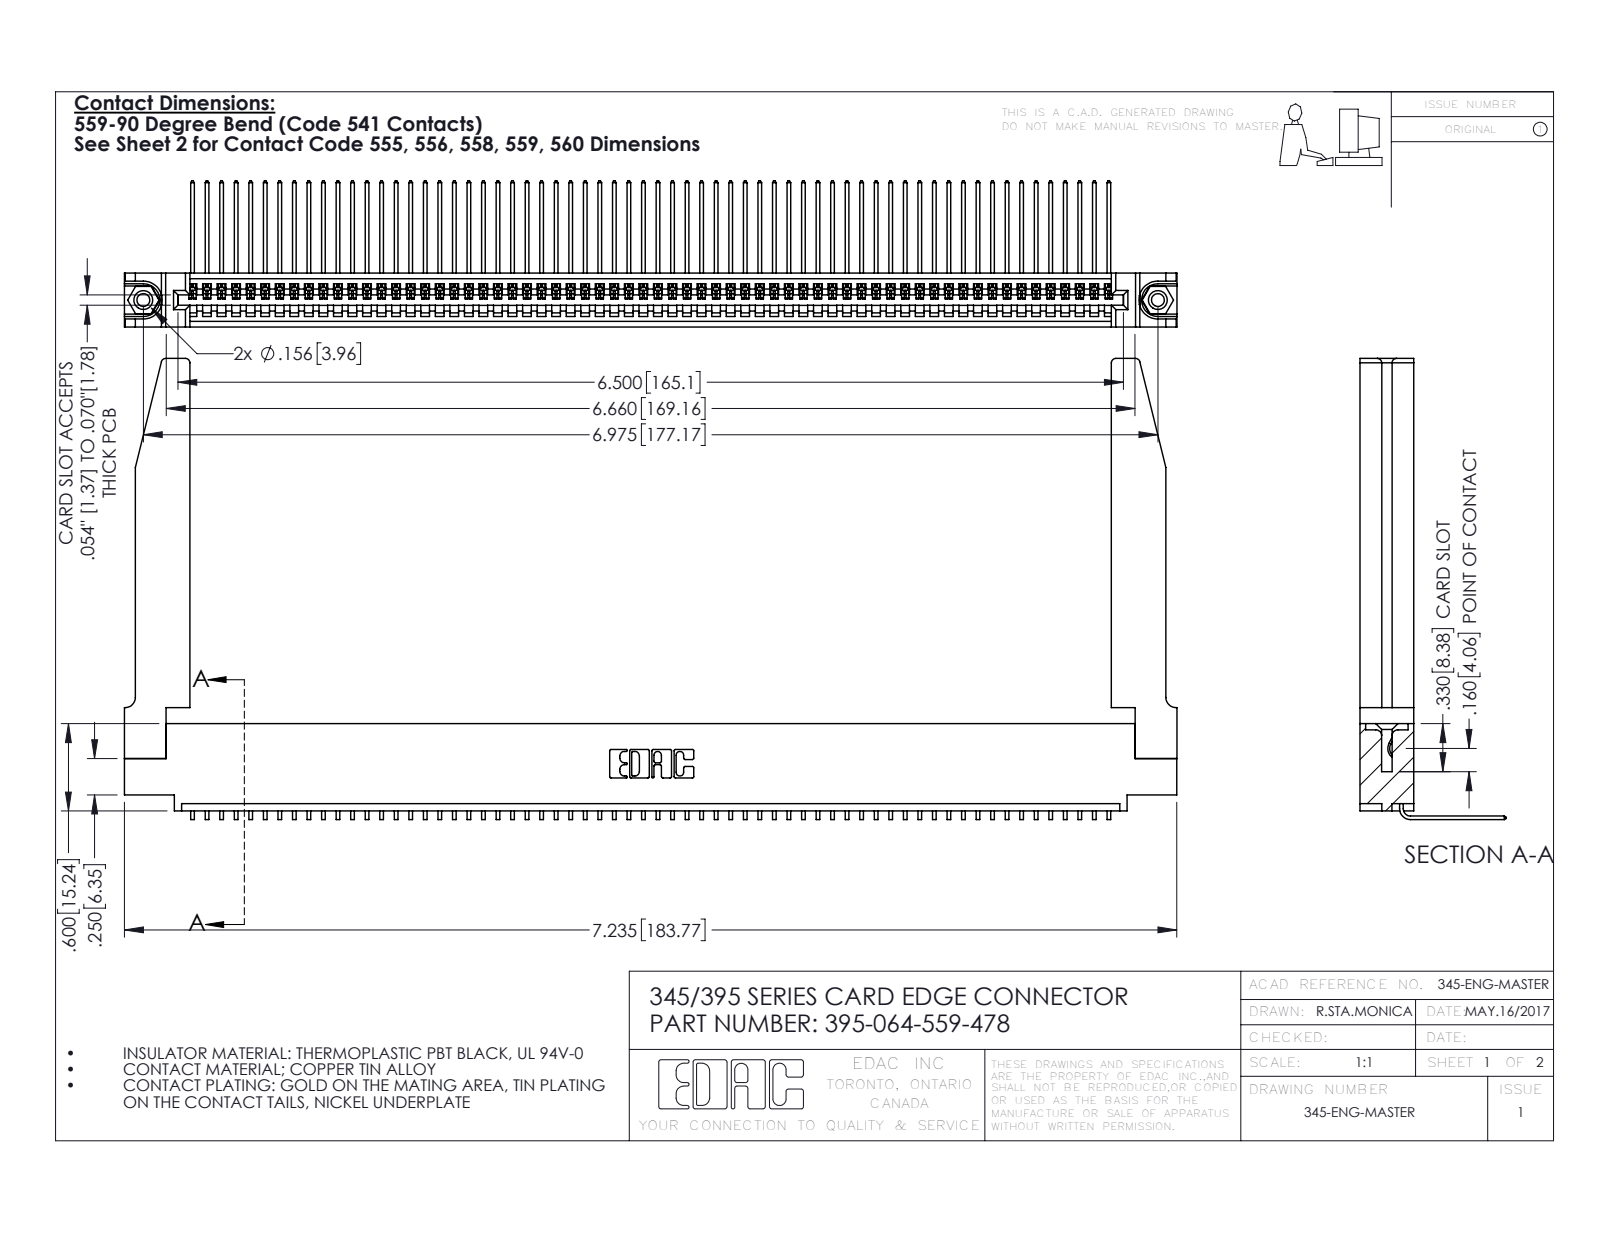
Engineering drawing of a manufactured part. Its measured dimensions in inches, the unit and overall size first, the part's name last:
Units: inches
Overall size (bounding box): 7.236 × 3.169 × 1.005
Round holes (diameter × count): ⌀0.089 ×2, ⌀0.125 ×2, ⌀0.156 ×2, ⌀0.064 ×1
Round bosses / shafts (diameter × count): ⌀0.155 ×2
Partial cylindrical surfaces — rounded edges, fillets, slot ends (radius × count): R0.006 ×128, R0.01 ×22, R0.03 ×8, R0.007 ×6, R0.031 ×6, R0.026 ×3, R0.031 ×2, R0.04 ×2
Main face-to-face distances: 0.37, 0.072, 0.298, 0.098, 0.272, 0.025, 0.2, 0.225, 0.148, 0.15
Hole centre spacings: 0.27, 6.739, 6.975
Volume: 1.559 in³ · Surface area: 49.76 in²
Bodies: 69 solids, 4204 faces (2914 planar, 1238 cylindrical, 52 other)
Part name (STEP PRODUCT): 345-250-001_345-250-001-102; 395-064-559-478; 345 Part_0.110 Offset - 0.156 Dia-TH; 345-220-078_345-220-078 (+1 more)
STEP written by: SolidWorks 2016 (CONFIG_CONTROL_DESIGN)
